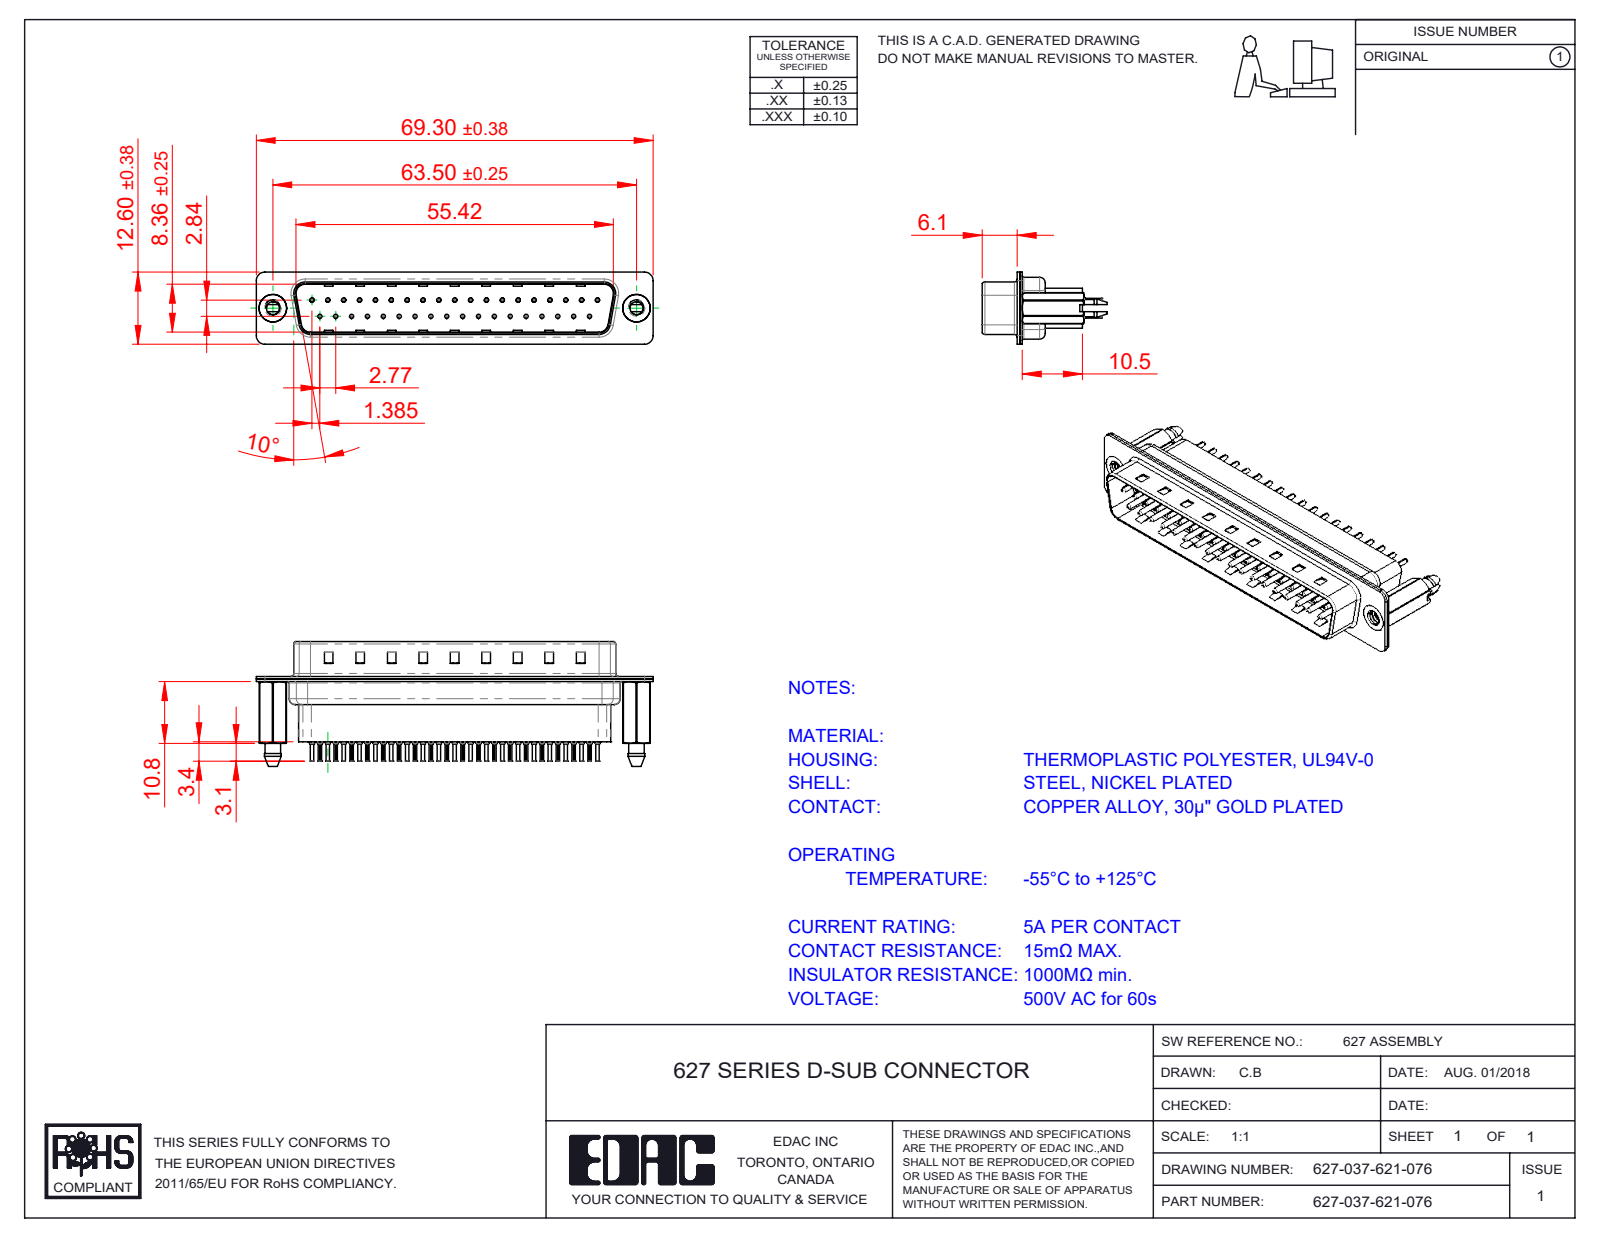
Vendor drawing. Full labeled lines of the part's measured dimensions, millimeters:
Part name (STEP PRODUCT): 627 Shell Rear_37 Contacts; 627 Contact Row 2_21H; 627-037-621-076; 627 Contact Row 1_21H (+3 more)
STEP written by: SolidWorks 2020 (CONFIG_CONTROL_DESIGN)
Units: millimetres
Bodies: 42 solids, 4152 faces (1123 planar, 1578 cylindrical, 1451 other)
Overall size (bounding box): 69.3 × 21.7 × 12.6
Volume: 5 558 mm³ · Surface area: 14 141 mm²
Round holes (diameter × count): ⌀0.2 ×37, ⌀0.35 ×37, ⌀1.1 ×37, ⌀1.6 ×37, ⌀2.26 ×2, ⌀4 ×2, ⌀4.8 ×2
Round bosses / shafts (diameter × count): ⌀2 ×37, ⌀1.5 ×37, ⌀0.75 ×37, ⌀0.6 ×37, ⌀4.9 ×2
Partial cylindrical surfaces — rounded edges, fillets, slot ends (radius × count): R0.1 ×74, R1.5 ×18, R2 ×12, R1.6 ×10, R0.5 ×8, R0.25 ×4, R0.6 ×4, R0.65 ×4
Main face-to-face distances: 0.4, 0.82, 9.58, 0.45, 0.68, 7.68, 1.5, 1.08, 8.08, 8.76
Hole centre spacings: 3.16, 2.77, 5.54, 8.31, 5.04, 10.1, 11.08, 12.78
